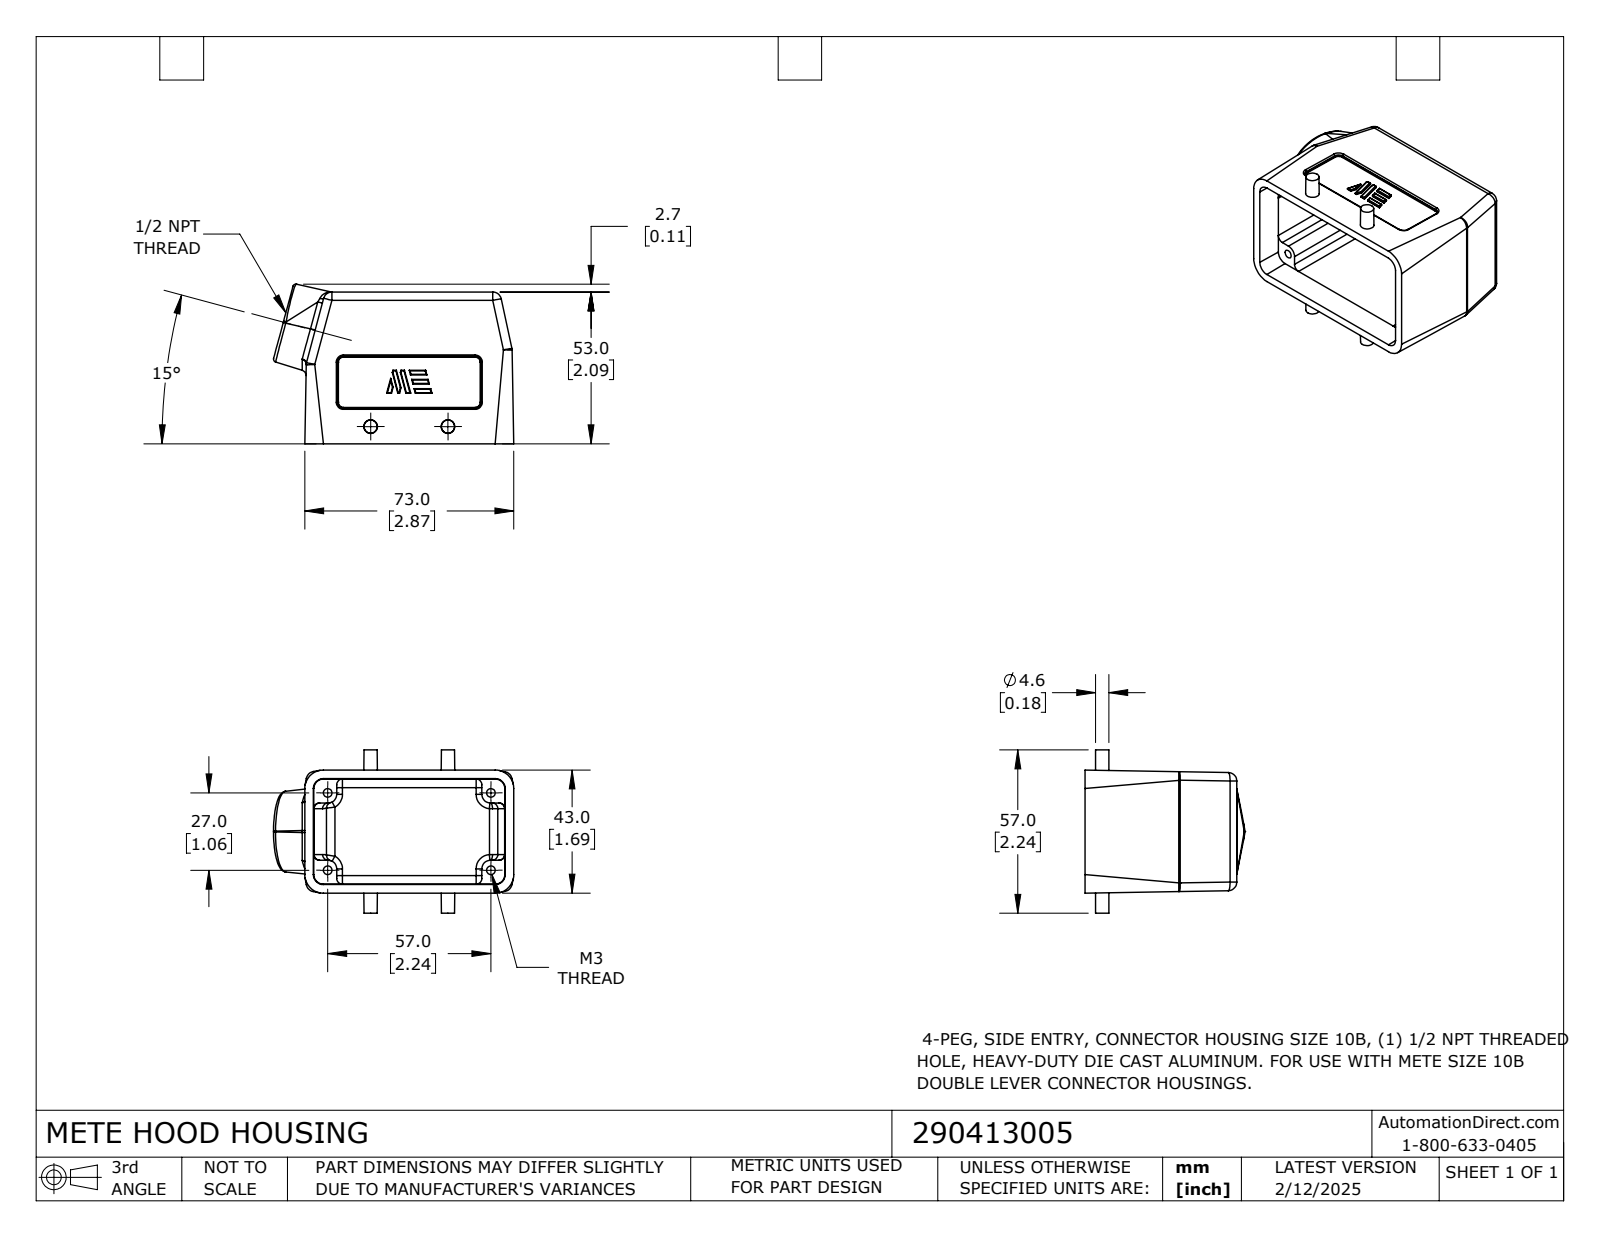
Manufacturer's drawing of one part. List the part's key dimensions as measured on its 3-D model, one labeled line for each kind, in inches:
Part name (STEP PRODUCT): 290413005
STEP written by: SolidWorks 2024 (CONFIG_CONTROL_DESIGN)
Units: inches
Bodies: 1 solid, 339 faces (122 planar, 130 cylindrical, 87 other)
Overall size (bounding box): 3.304 × 2.244 × 2.194
Volume: 3.229 in³ · Surface area: 43.92 in²
Round holes (diameter × count): ⌀0.118 ×4
Partial cylindrical surfaces — rounded edges, fillets, slot ends (radius × count): R0.008 ×43, R0.079 ×22, R0.118 ×18, R0.02 ×8, R0.075 ×4, R0.039 ×3, R0.098 ×2
Main face-to-face distances: 1.444, 0.118, 0.04, 0.157, 0.078, 1.929, 2.087, 0.315, 2.31, 0.079
Hole centre spacings: 1.063, 2.244, 2.483
